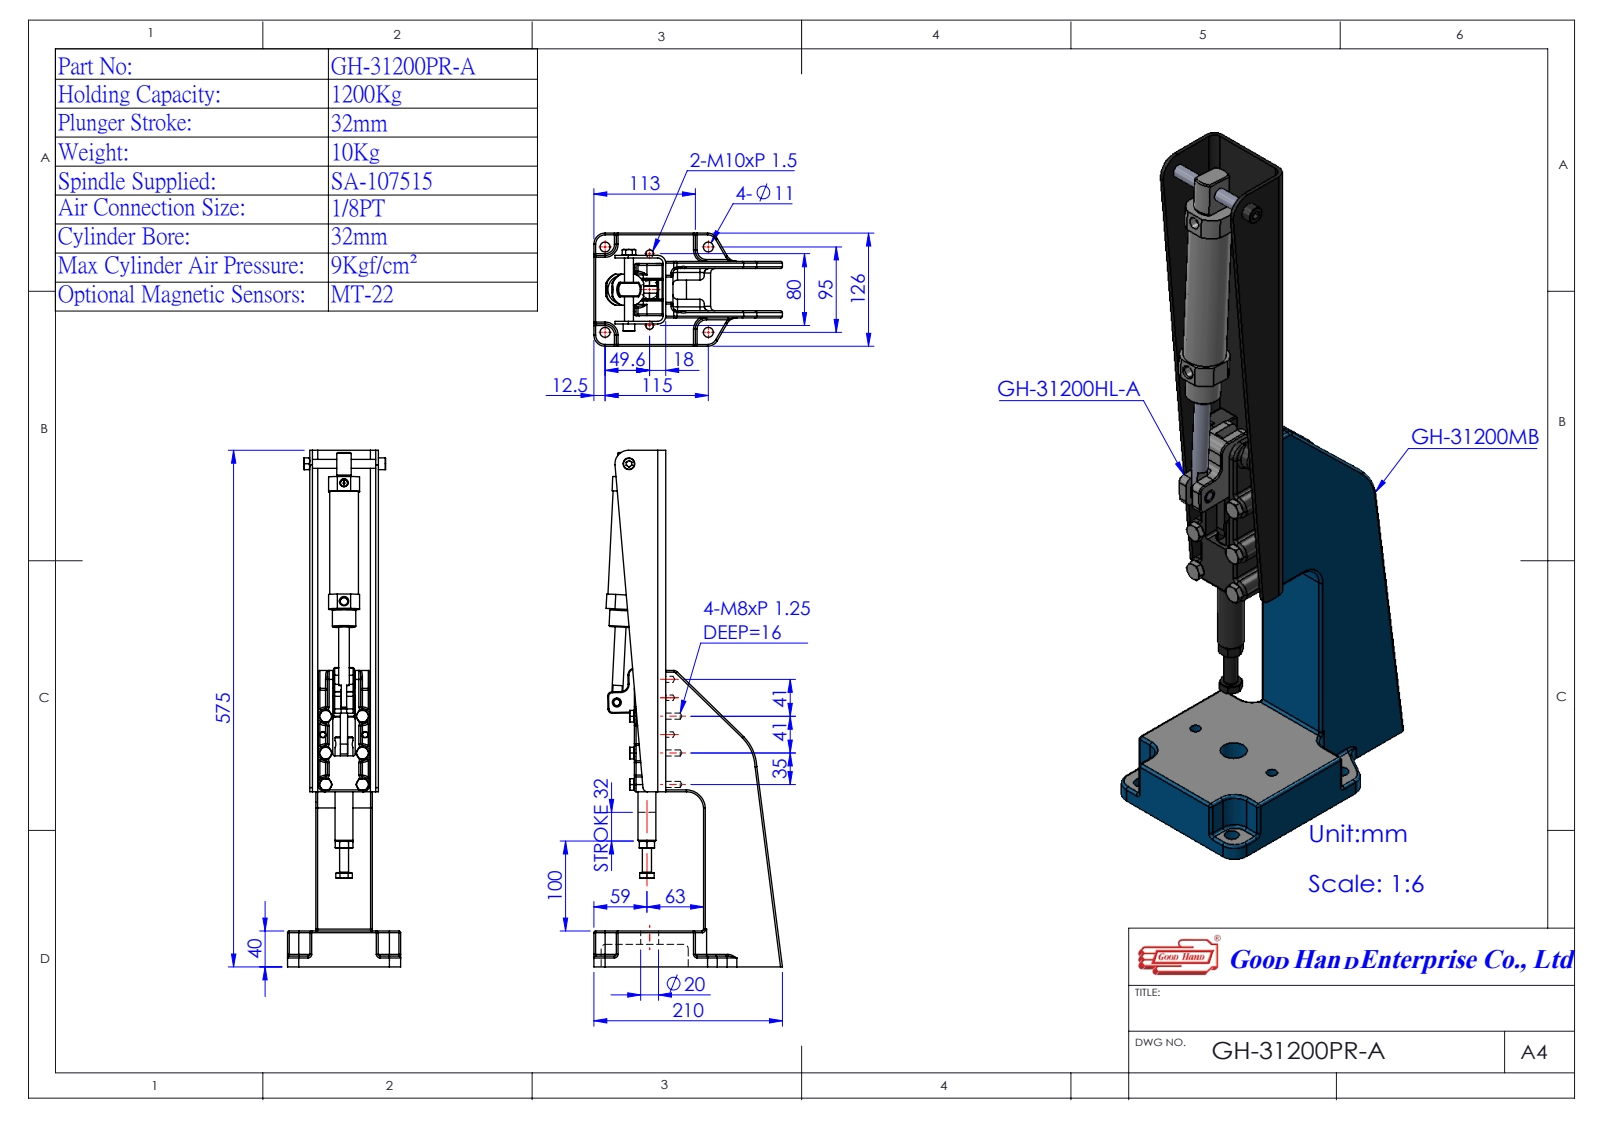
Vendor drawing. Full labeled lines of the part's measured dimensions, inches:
Part name (STEP PRODUCT): Group3^GH-31200HL-A(簡化); Group1^GH-31200HL-A(簡化); GH-31200MB; GH-31200PR-A(簡化) (+6 more)
STEP written by: SolidWorks 2016 (AUTOMOTIVE_DESIGN)
Units: inches
Bodies: 8 solids, 1083 faces (341 planar, 353 cylindrical, 389 other)
Overall size (bounding box): 22.638 × 8.268 × 4.961
Volume: 80.92 in³ · Surface area: 634.1 in²
Round holes (diameter × count): ⌀0.236 ×8, ⌀0.268 ×8, ⌀0.335 ×4, ⌀0.437 ×4, ⌀0.311 ×2, ⌀0.394 ×1, ⌀0.472 ×1, ⌀0.591 ×1, ⌀0.785 ×1, ⌀0.787 ×1, ⌀1.181 ×1
Round bosses / shafts (diameter × count): ⌀0.512 ×7, ⌀1.26 ×1, ⌀1.024 ×1, ⌀0.984 ×1, ⌀0.784 ×1, ⌀0.63 ×1, ⌀0.472 ×1, ⌀0.394 ×1
Partial cylindrical surfaces — rounded edges, fillets, slot ends (radius × count): R0.079 ×75, R0.197 ×34, R0.039 ×17, R0.492 ×13, R0.315 ×6, R0.335 ×6, R0.394 ×6, R0.354 ×3
Main face-to-face distances: 0.315, 0.118, 2.165, 2.894, 0.148, 0.463, 2.313, 2.628, 0.266, 0.581
Hole centre spacings: 1.614, 0.816, 1.911, 2.283, 2.424, 2.977, 1.378, 1.575
